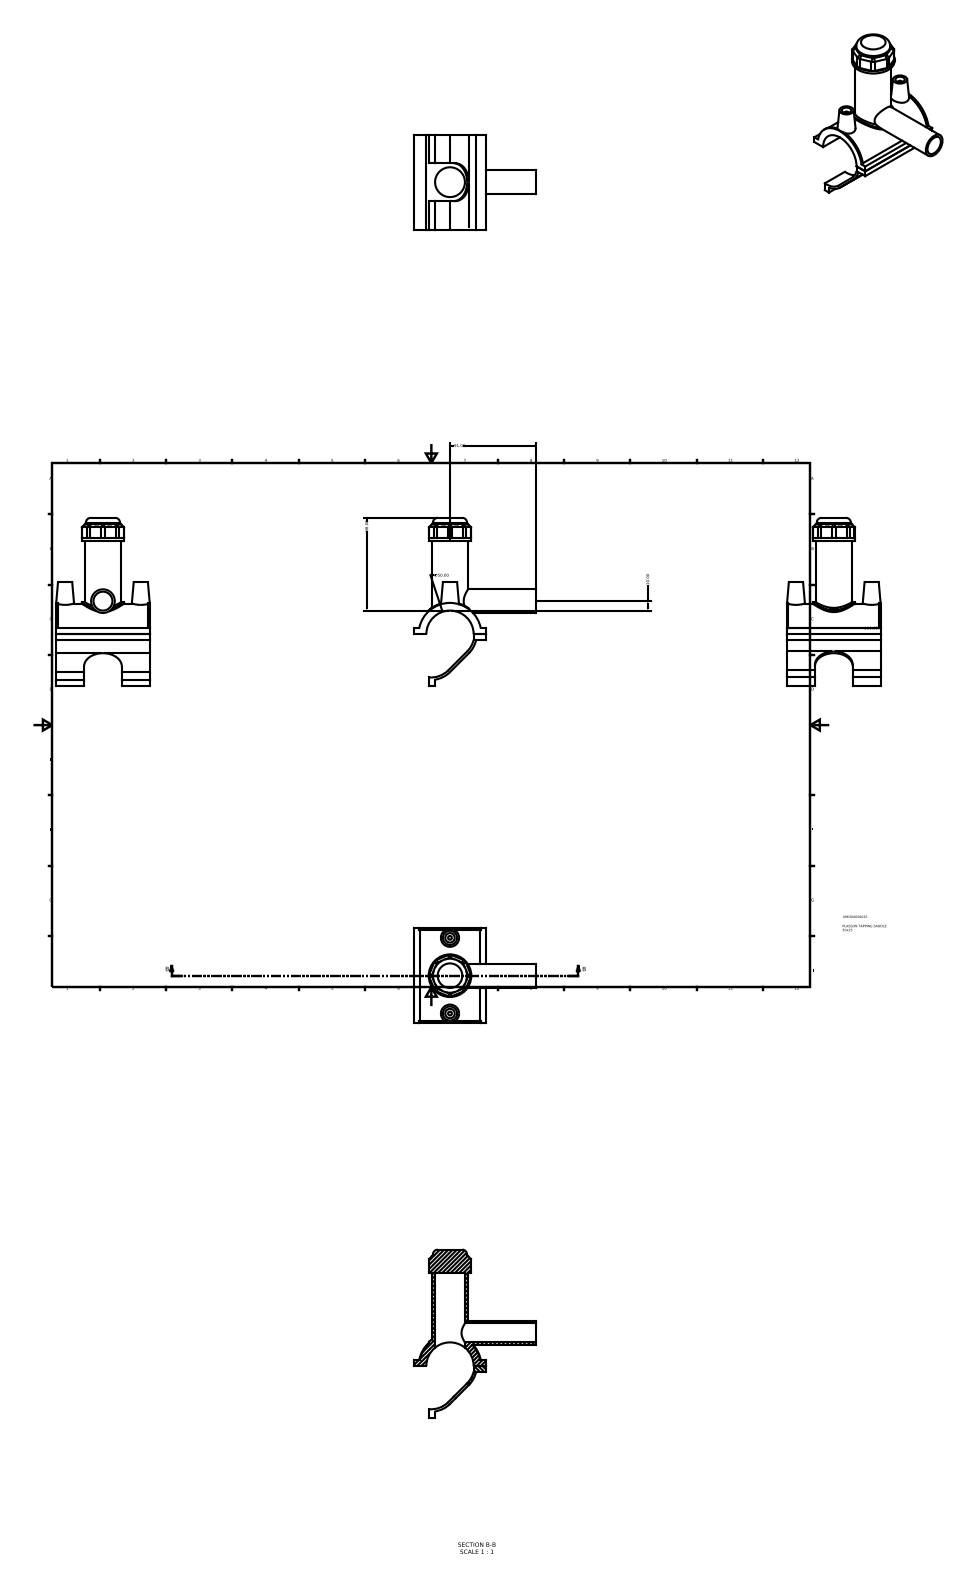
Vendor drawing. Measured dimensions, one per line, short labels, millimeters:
name: 496304050025
written by: Autodesk Inventor 2015 (AUTOMOTIVE_DESIGN)
unit: mm
bodies: 2 solids, 111 faces (66 planar, 32 cylindrical, 13 other)
size: 177.37 × 129 × 100
volume: 169 305 mm³; area: 71 199 mm²
holes: 2× ⌀10, 1× ⌀20, 1× ⌀31.5
bosses: 2× ⌀4, 1× ⌀45, 1× ⌀38.25, 1× ⌀36, 1× ⌀25
rounds: 8× R5, 2× R25.68, 2× R28.28, 1× R20, 1× R21.38, 1× R25, 1× R32.5, 1× R33.15
face distances: 6.2, 2.6, 98.45, 92.25, 100, 12.4, 104.65, 76, 41.58, 63
hole spacings: 40, 80
